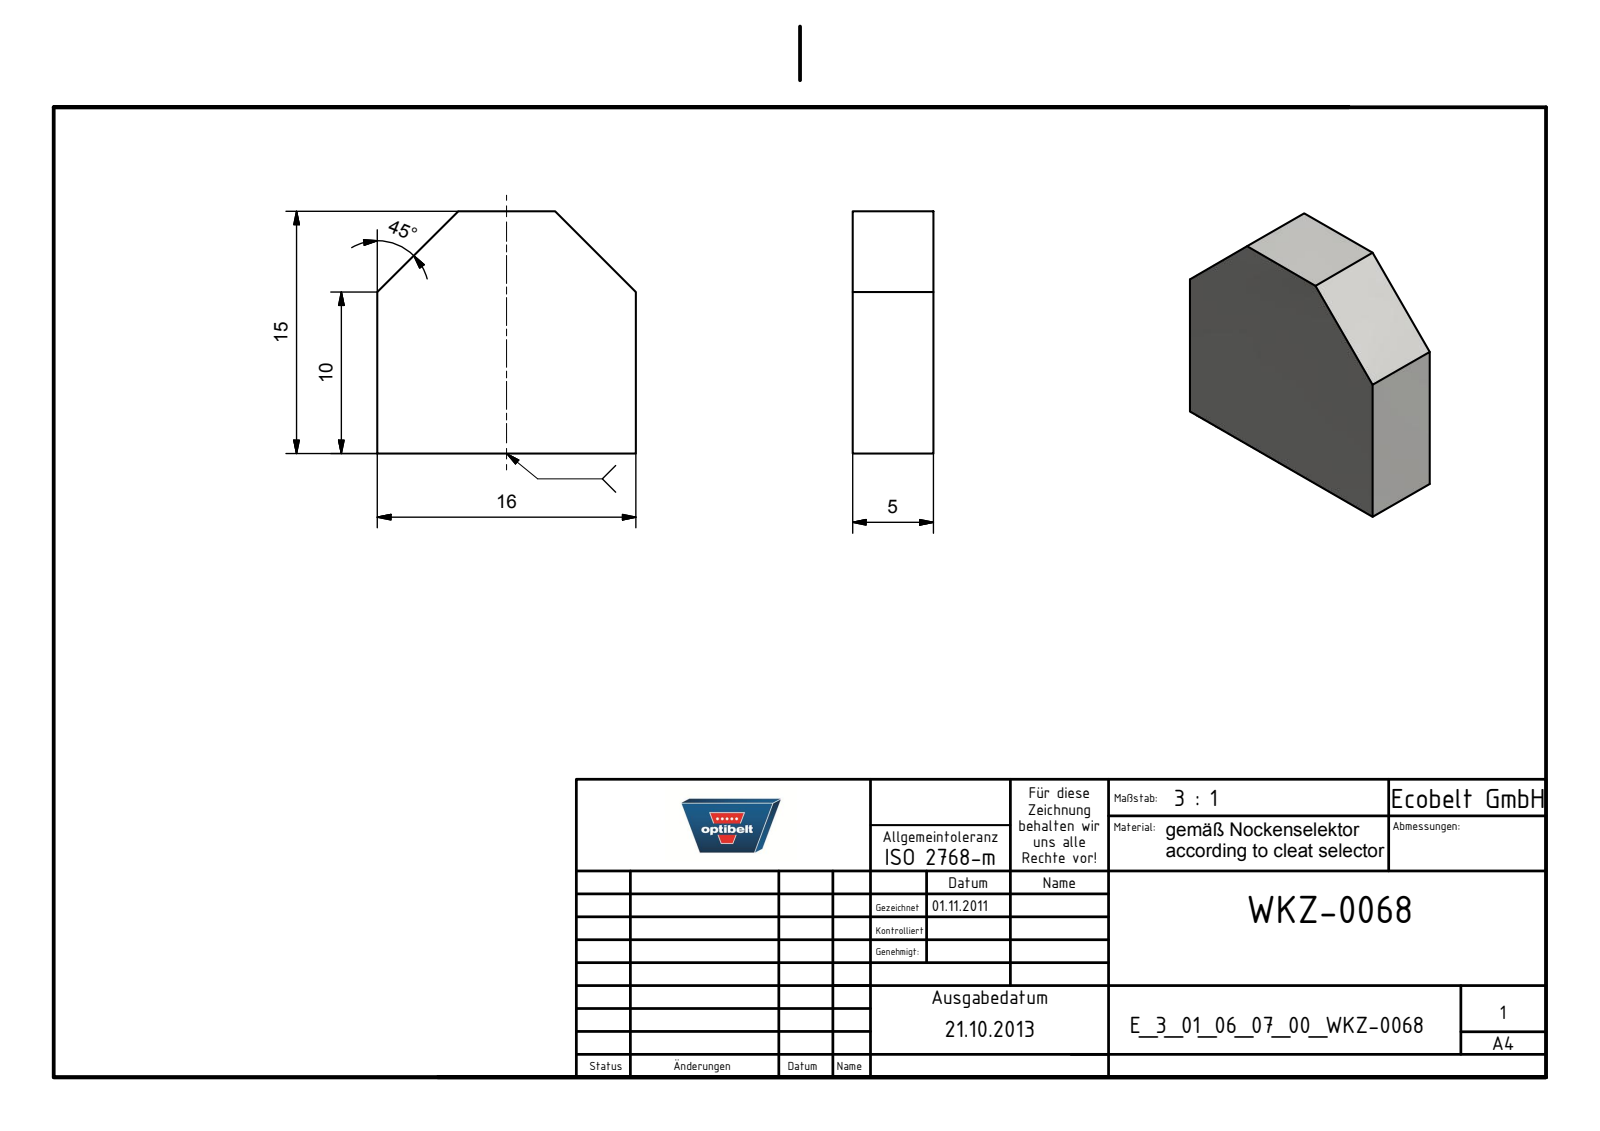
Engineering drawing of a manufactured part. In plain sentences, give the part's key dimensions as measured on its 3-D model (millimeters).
The part is named "E_3_01_06_07_00_WKZ-0068". Its 3-D file was written by "Autodesk Inventor 2025 (AUTOMOTIVE_DESIGN)". It is 1 solid with 8 faces: 8 planar, 0 cylindrical and 0 other. Overall it measures 16 by 15 by 5 millimeters. Its volume is 1 075 cubic millimeters and its surface area 711 square millimeters. The main face-to-face distances are 5, 16, 15.
